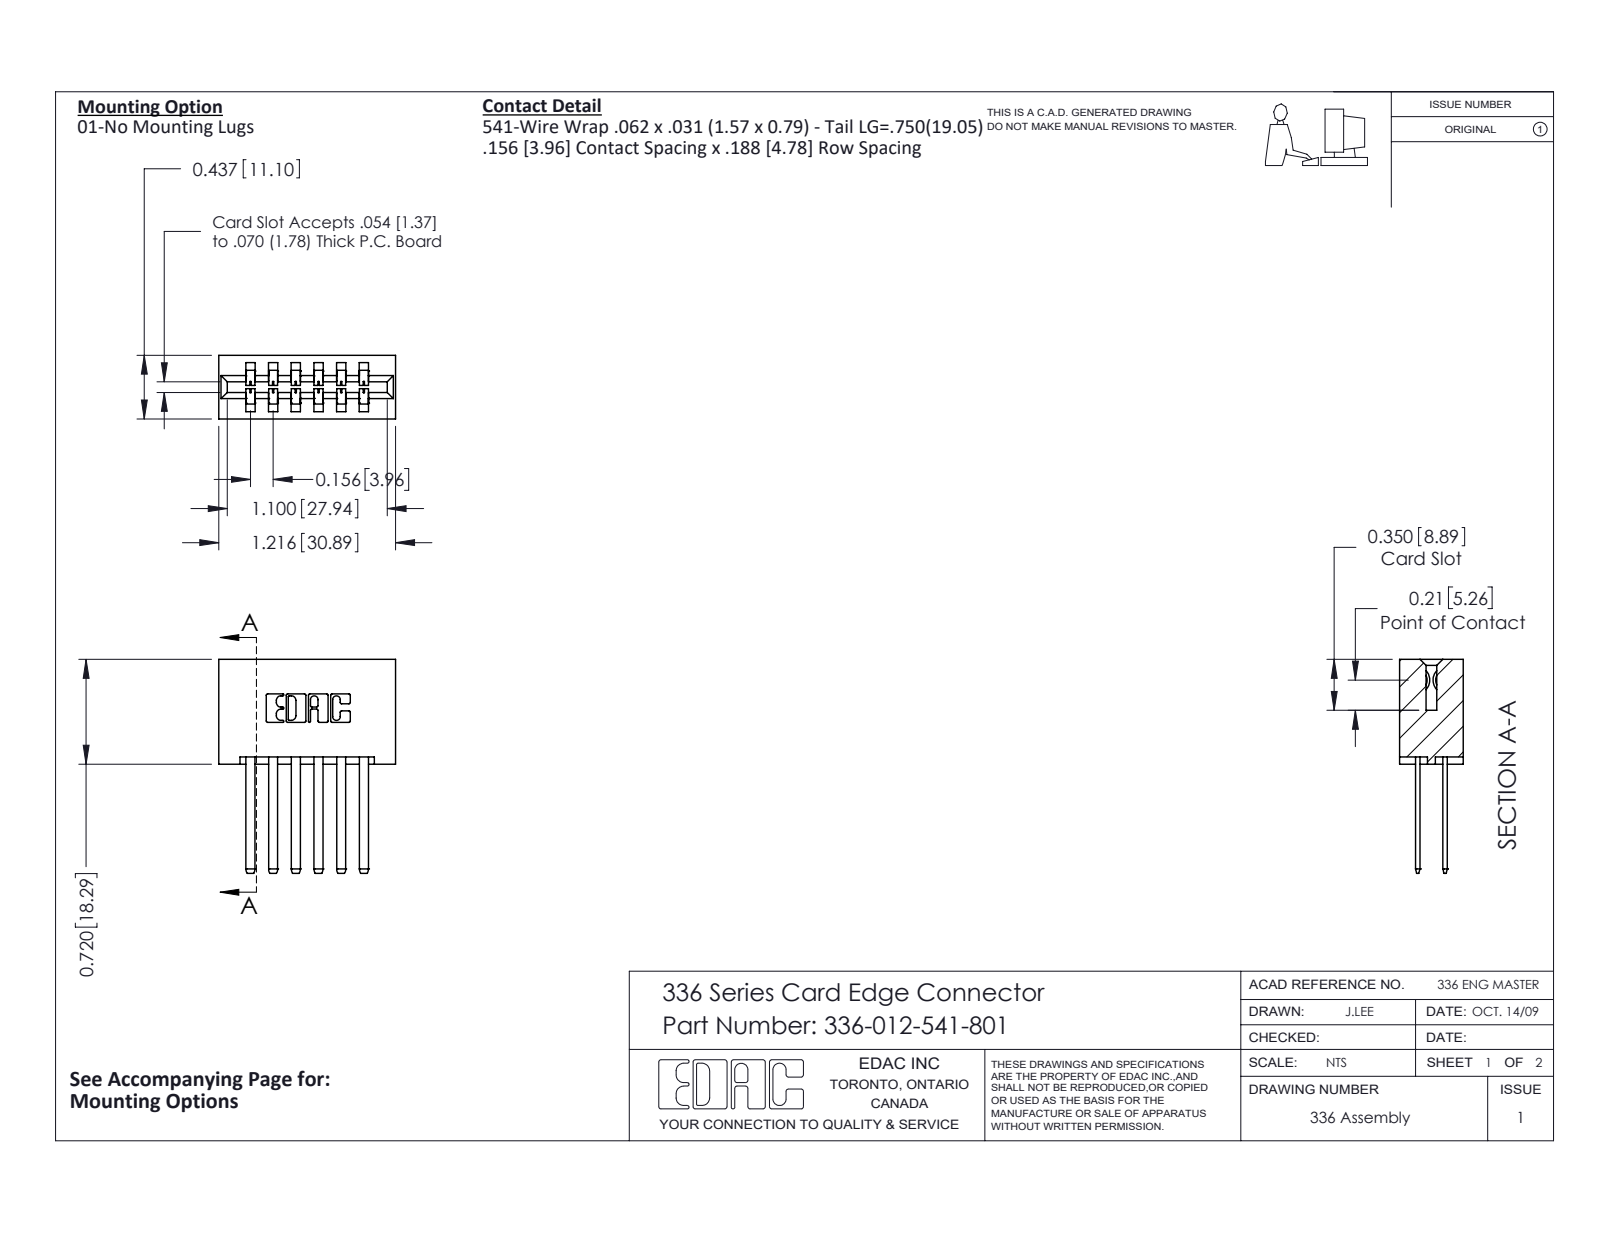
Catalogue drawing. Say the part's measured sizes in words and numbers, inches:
The part is named "336-290-001_336-290-541; 336-012-541-801; 336 Part_Lugless". Its 3-D file was written by "SolidWorks 2020 (CONFIG_CONTROL_DESIGN)". It is 13 solids with 610 faces: 378 planar, 232 cylindrical and 0 other. Overall it measures 1.47 by 1.216 by 0.437 inches. Its volume is 0.32 cubic inches and its surface area 9.434 square inches. Partial cylindrical surfaces (rounded edges, fillets, slot ends): 24 of radius 0.004, 22 of radius 0.01, 12 of radius 0.056, 6 of radius 0.007, 6 of radius 0.031, 4 of radius 0.022, 4 of radius 0.04, 3 of radius 0.026. The main face-to-face distances are 0.156, 0.188, 0.437, 0.328, 0.14, 0.297, 0.109, 0.031, 0.219, 0.312.
